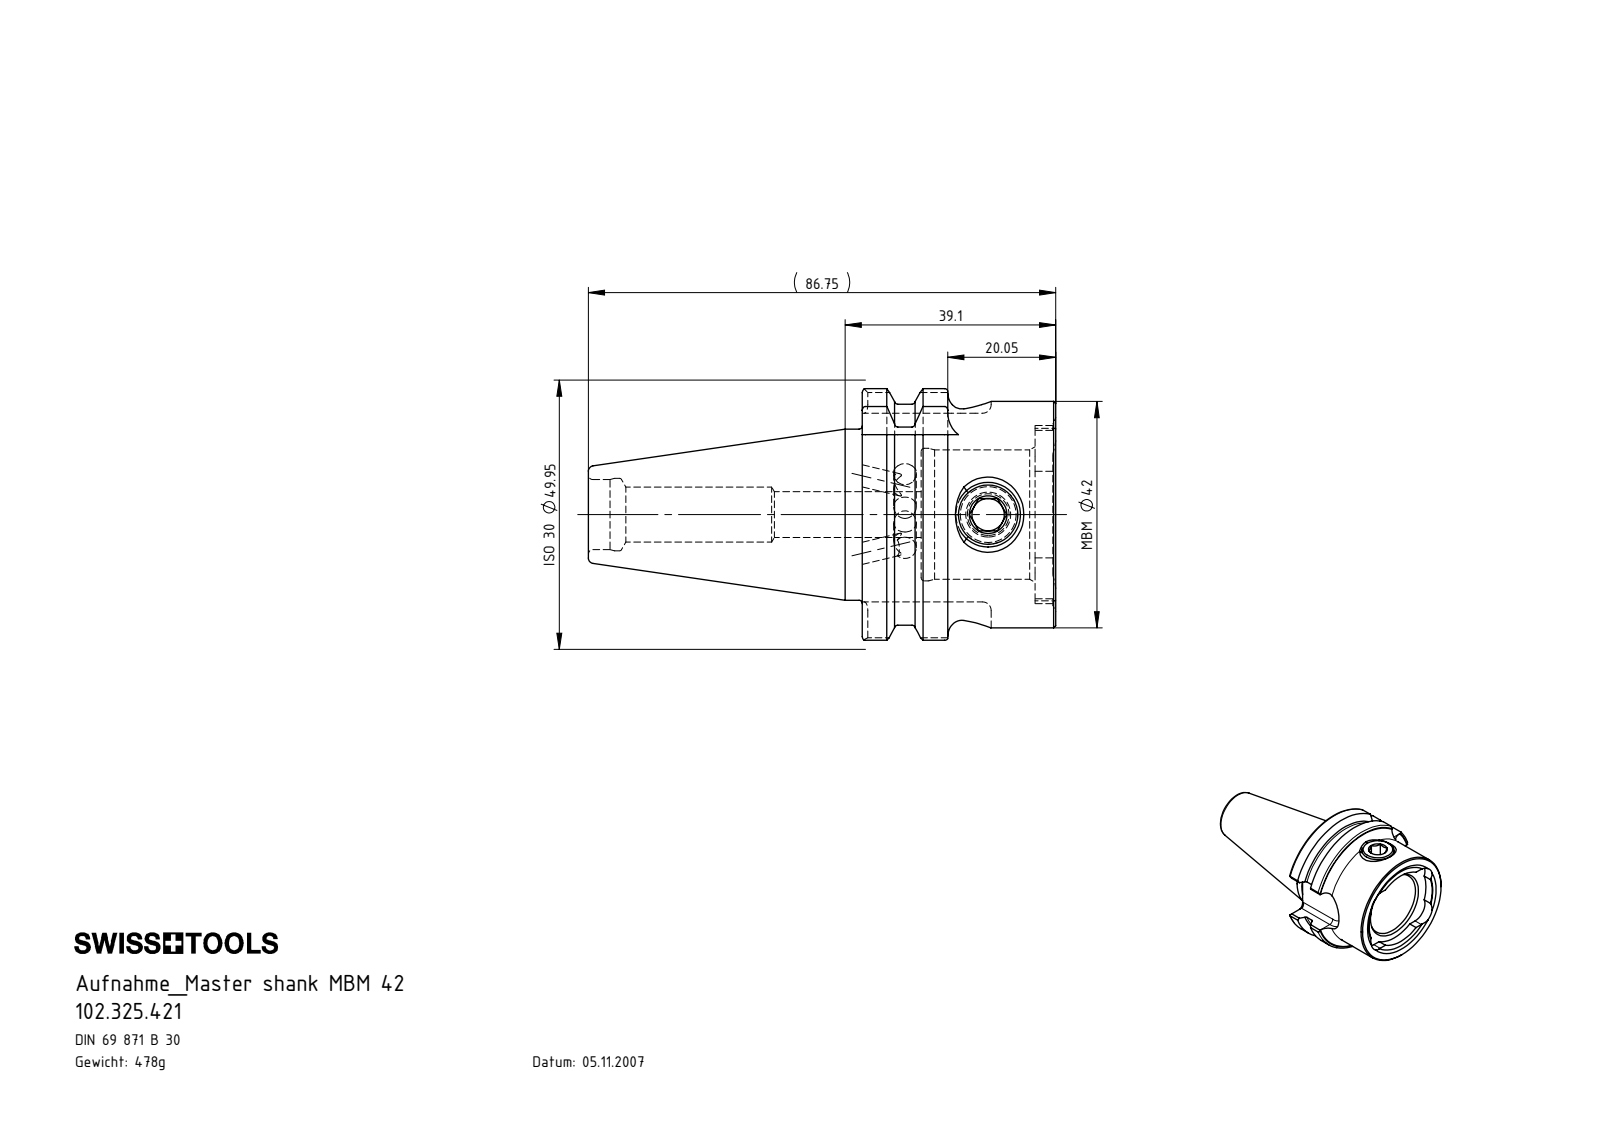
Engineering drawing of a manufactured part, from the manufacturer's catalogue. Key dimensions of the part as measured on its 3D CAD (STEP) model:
Part name (STEP PRODUCT): 102.325.421; SB3-MB4.K01.039_C_mit Bundkhlung; MB4-ER1.001.013_A
STEP written by: SolidWorks 2017 (CONFIG_CONTROL_DESIGN)
Units: millimetres
Bodies: 2 solids, 198 faces (51 planar, 65 cylindrical, 82 other)
Overall size (bounding box): 86.75 × 49.95 × 46.69
Volume: 60 905 mm³ · Surface area: 17 655 mm²
Round holes (diameter × count): ⌀4 ×2, ⌀4.2 ×1, ⌀6 ×1, ⌀8.5 ×1, ⌀10.2 ×1, ⌀11 ×1, ⌀13 ×1, ⌀13.45 ×1, ⌀24 ×1, ⌀24.6 ×1
Round bosses / shafts (diameter × count): ⌀42 ×1, ⌀31.75 ×1, ⌀12 ×1
Partial cylindrical surfaces — rounded edges, fillets, slot ends (radius × count): R1.6 ×8, R5.2 ×4, R8 ×1, R8.05 ×1, R14.9 ×1, R16.52 ×1, R22.02 ×1, R24.98 ×1
Main face-to-face distances: 10.9, 32.05, 21.15, 35.9, 25, 3.85, 35, 16.1, 35.35, 24.45
